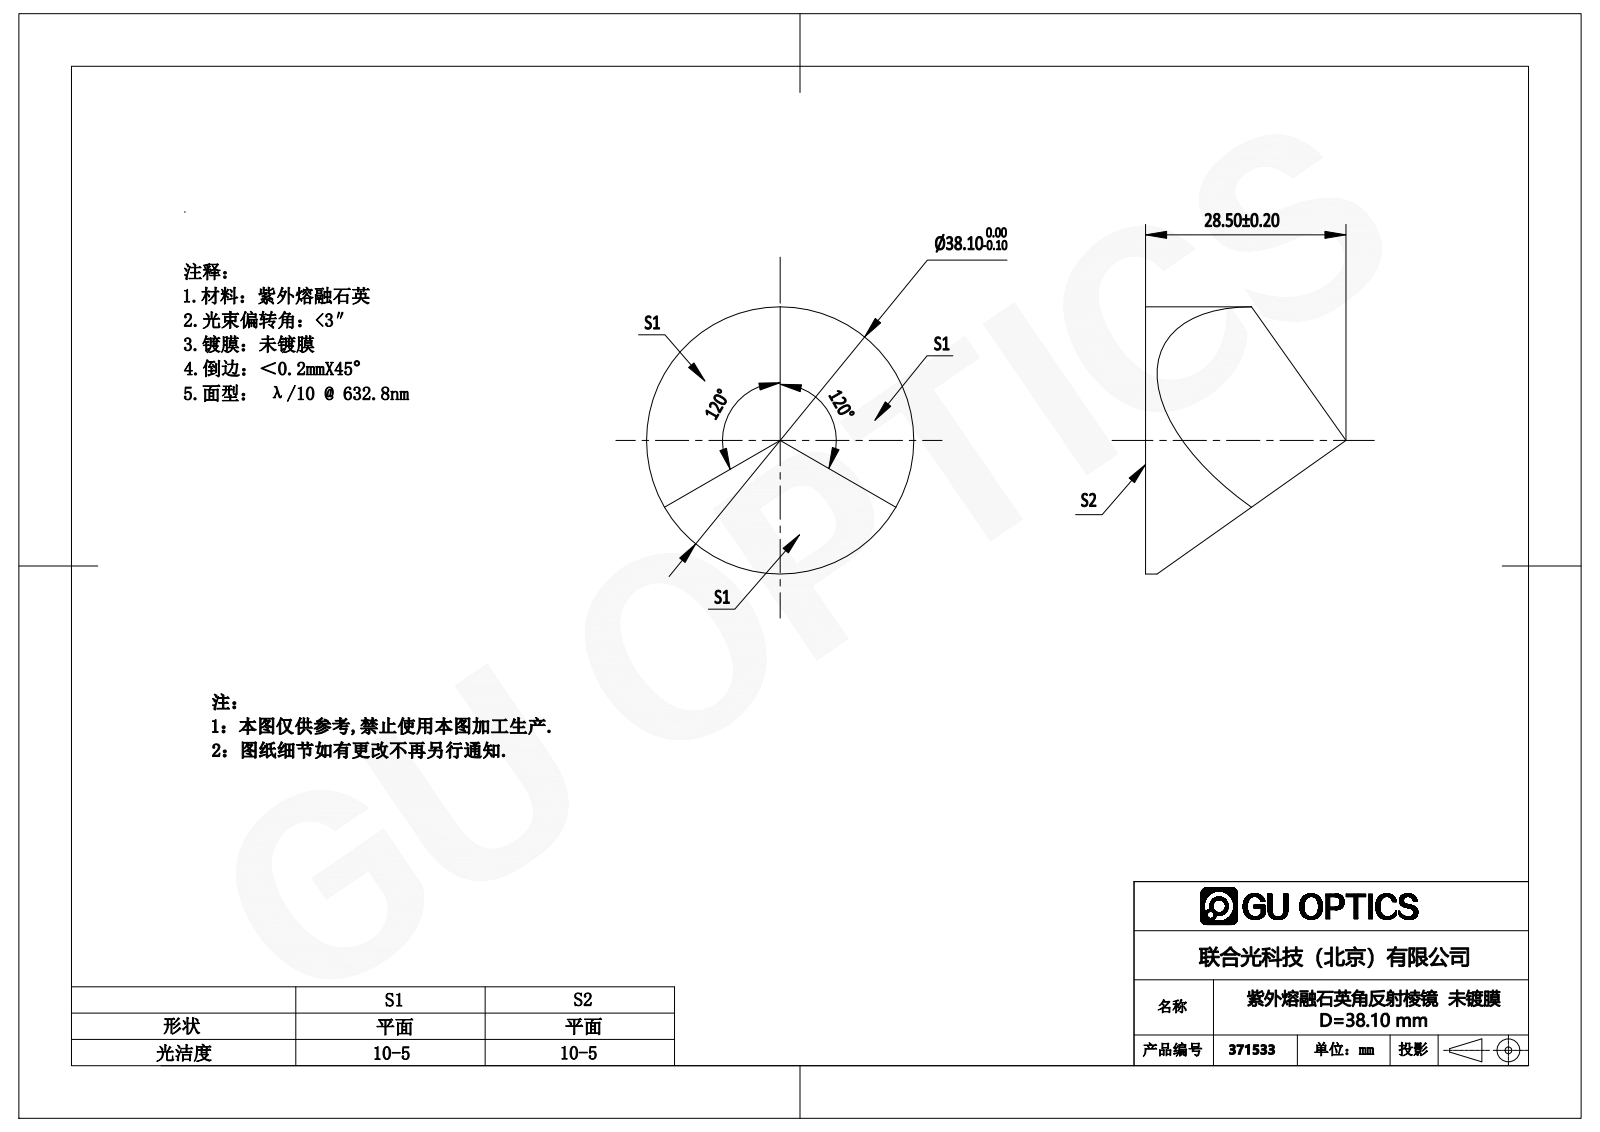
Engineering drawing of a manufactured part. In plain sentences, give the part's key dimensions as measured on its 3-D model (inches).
The part is named "371533". Its 3-D file was written by "SolidWorks 2016 (CONFIG_CONTROL_DESIGN)". It is 1 solid with 6 faces: 4 planar, 2 cylindrical and 0 other. Overall it measures 1.5 by 1.5 by 1.122 inches. Its volume is 0.95 cubic inches and its surface area 5.983 square inches. Round bosses or shafts: 1 of diameter 1.5.
